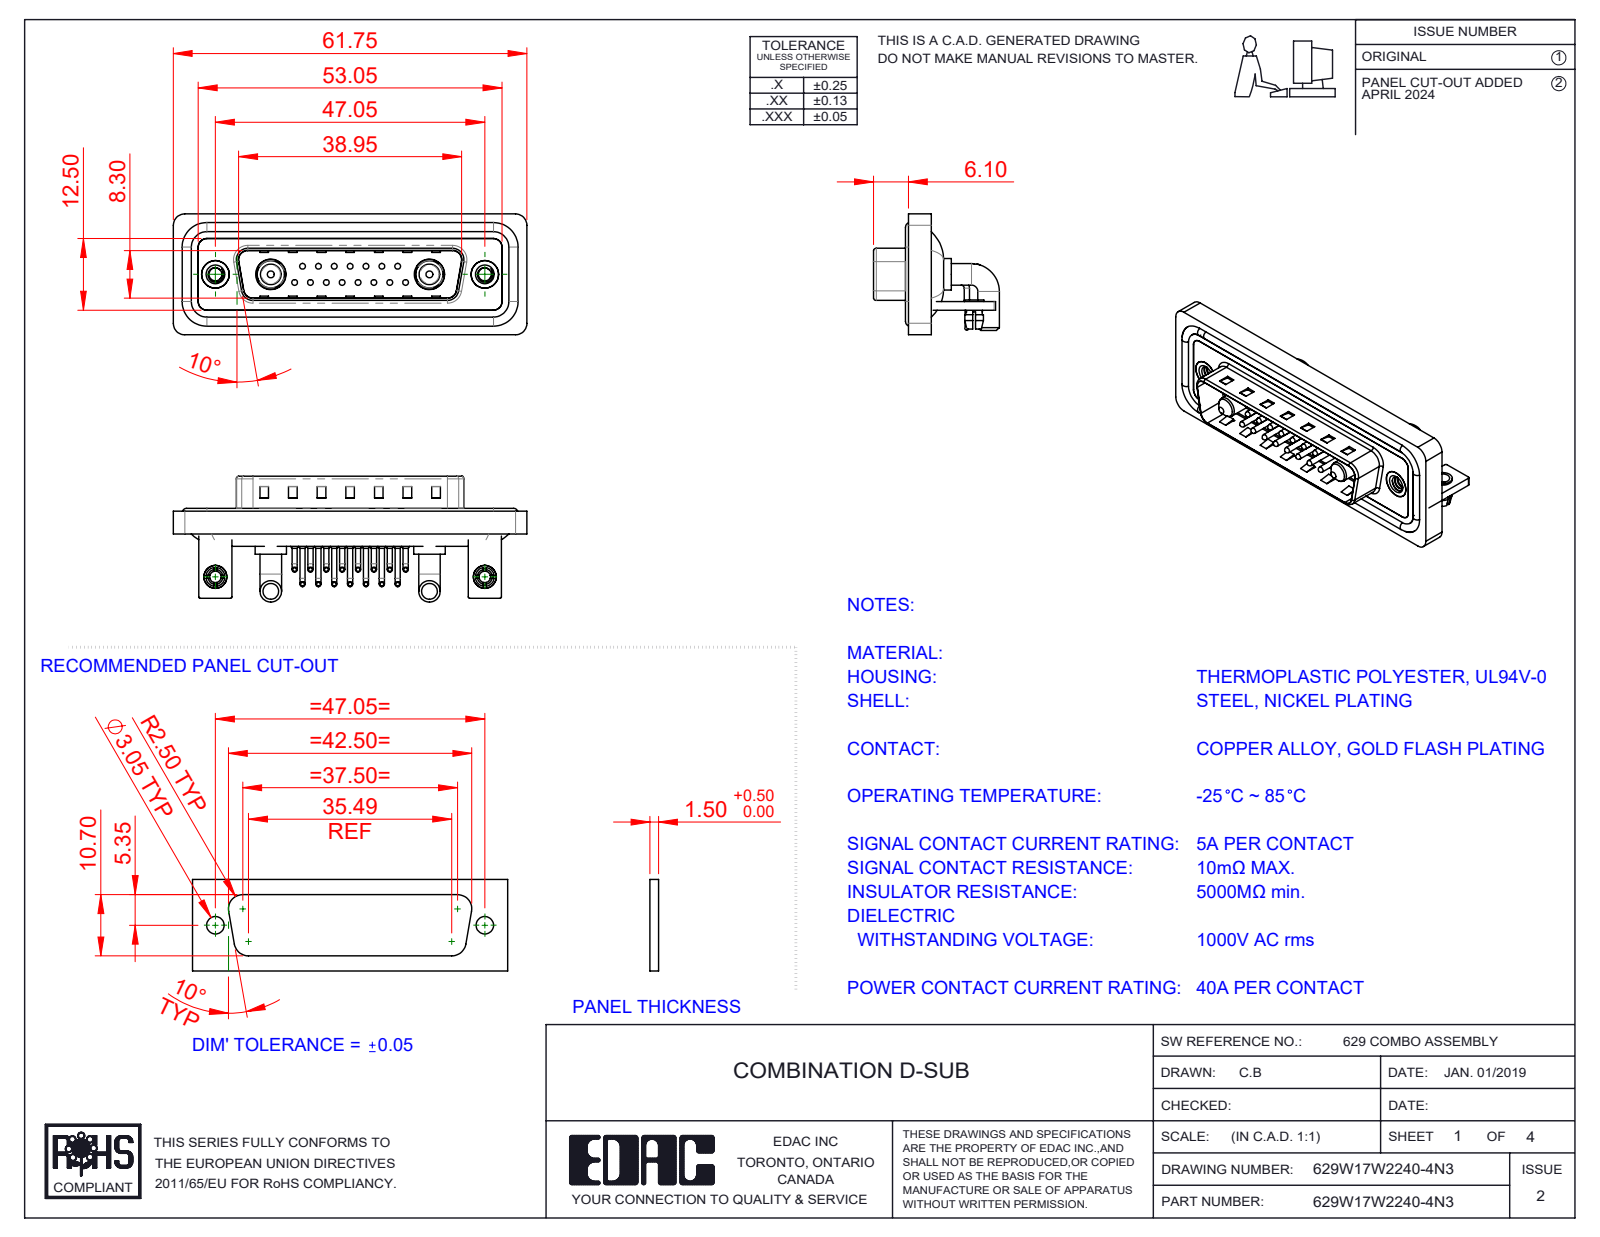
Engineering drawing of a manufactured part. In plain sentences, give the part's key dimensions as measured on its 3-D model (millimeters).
The part is named "629Combo Contact Row 2; 629Combo Housing_17W2; 629Combo Board Lock; 629Combo Shell Front_25 Contacts (+7 more)". Its 3-D file was written by "SolidWorks 2023 (CONFIG_CONTROL_DESIGN)". It is 30 solids with 2351 faces: 1257 planar, 820 cylindrical and 274 other. Overall it measures 61.75 by 21.98 by 21.1 millimeters. Its volume is 7 972 cubic millimeters and its surface area 13 486 square millimeters. Round holes: 17 of diameter 2, 15 of diameter 0.75, 15 of diameter 1.6, 2 of diameter 2.26, 2 of diameter 2.5, 2 of diameter 3.2, 2 of diameter 4, 2 of diameter 4.8, 2 of diameter 4.85, 2 of diameter 5, 2 of diameter 5.3. Round bosses or shafts: 30 of diameter 0.9, 15 of diameter 1.5, 15 of diameter 1, 15 of diameter 0.65, 4 of diameter 3.75, 4 of diameter 1.6, 2 of diameter 5.5, 2 of diameter 5.2. Partial cylindrical surfaces (rounded edges, fillets, slot ends): 19 of radius 2, 18 of radius 1.5, 16 of radius 0.25, 15 of radius 1.01, 9 of radius 0.5, 8 of radius 1.6, 4 of radius 0.6, 4 of radius 0.65. The main face-to-face distances are 0.4, 0.8, 2.1, 1.5, 2.9, 1.1, 4.1, 1.6, 4.5, 3.7. The hole center spacings are 3.16, 2.77, 5.54, 8.31, 5.04, 7.49, 11.08, 5.03.
